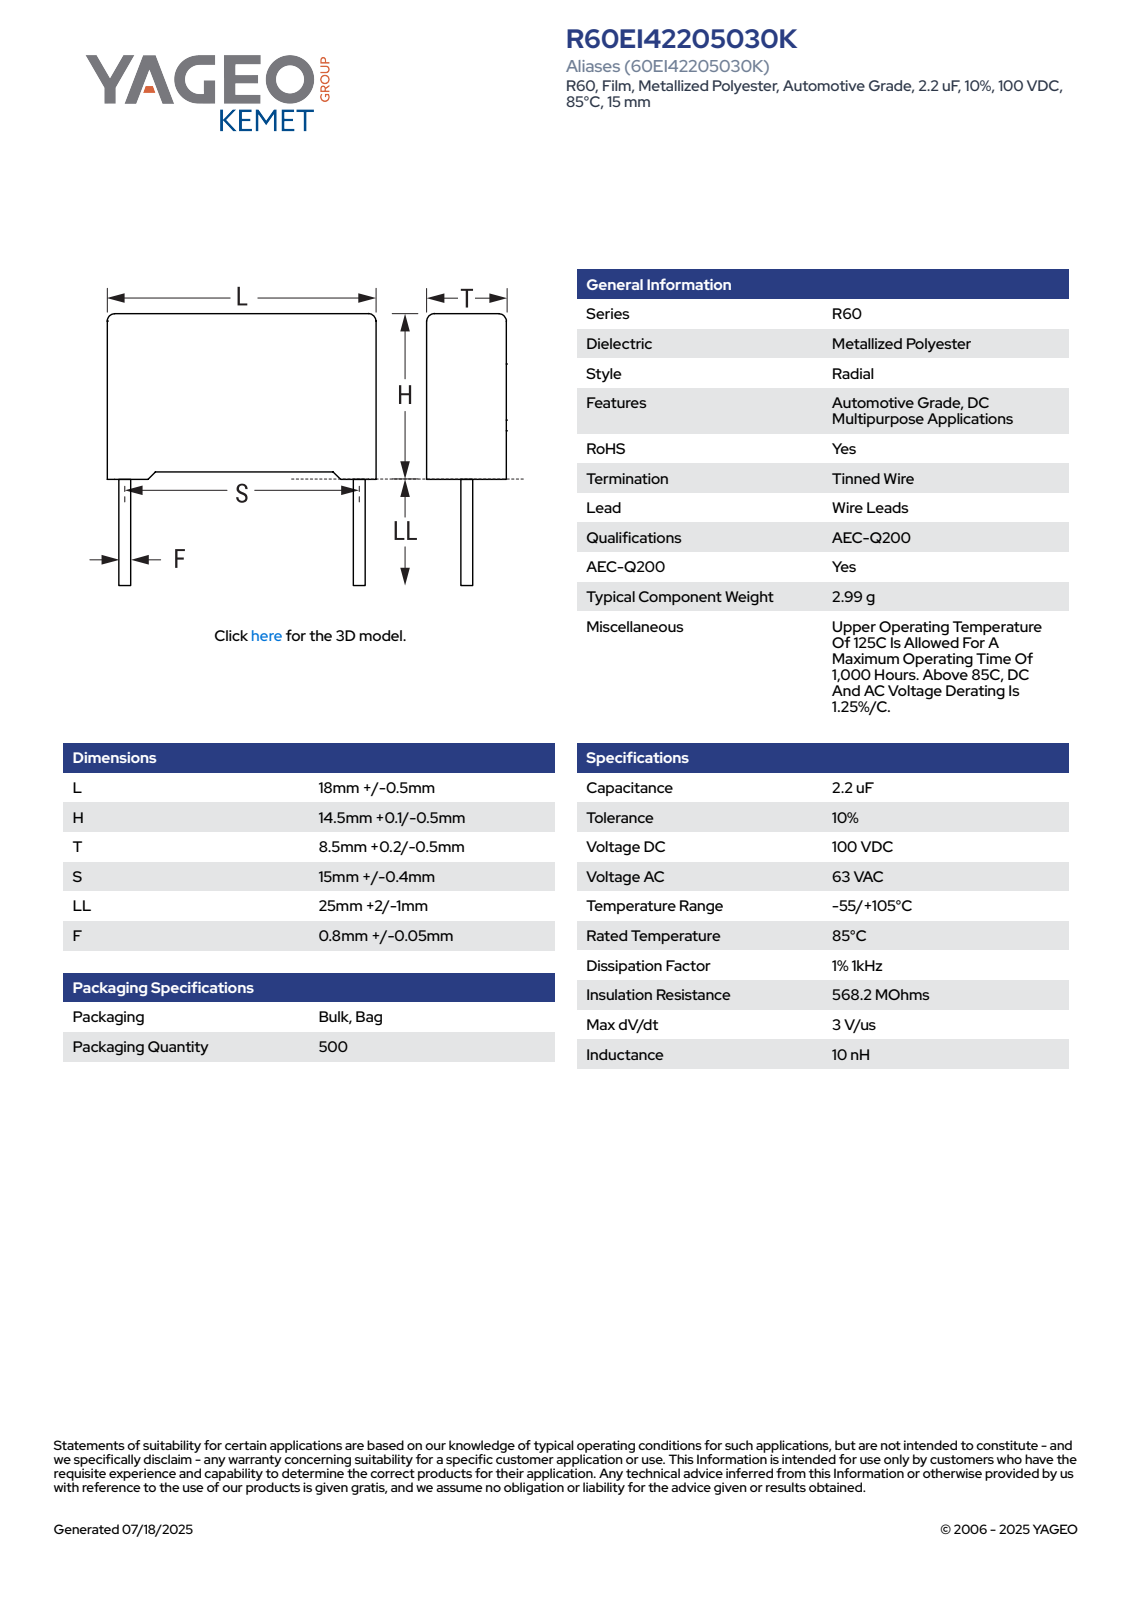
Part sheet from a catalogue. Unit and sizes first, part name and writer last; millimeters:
Units: millimetres
Overall size (bounding box): 41.6 × 18.5 × 8.71
Round bosses / shafts (diameter × count): ⌀0.85 ×2
Partial cylindrical surfaces — rounded edges, fillets, slot ends (radius × count): R0.5 ×4
Main face-to-face distances: 8.7, 13.85, 18.5, 0.62, 0.75, 14.6, 8.08, 0.5, 14.1, 17.88
Volume: 2 275 mm³ · Surface area: 1 293 mm²
Bodies: 4 solids, 85 faces (77 planar, 8 cylindrical, 0 other)
Part name (STEP PRODUCT): CFR_RB2_18X14.5X8.5_L18.5H14.6T8.7S15LL27F0.85
STEP written by: SolidWorks 2021 (AUTOMOTIVE_DESIGN)
